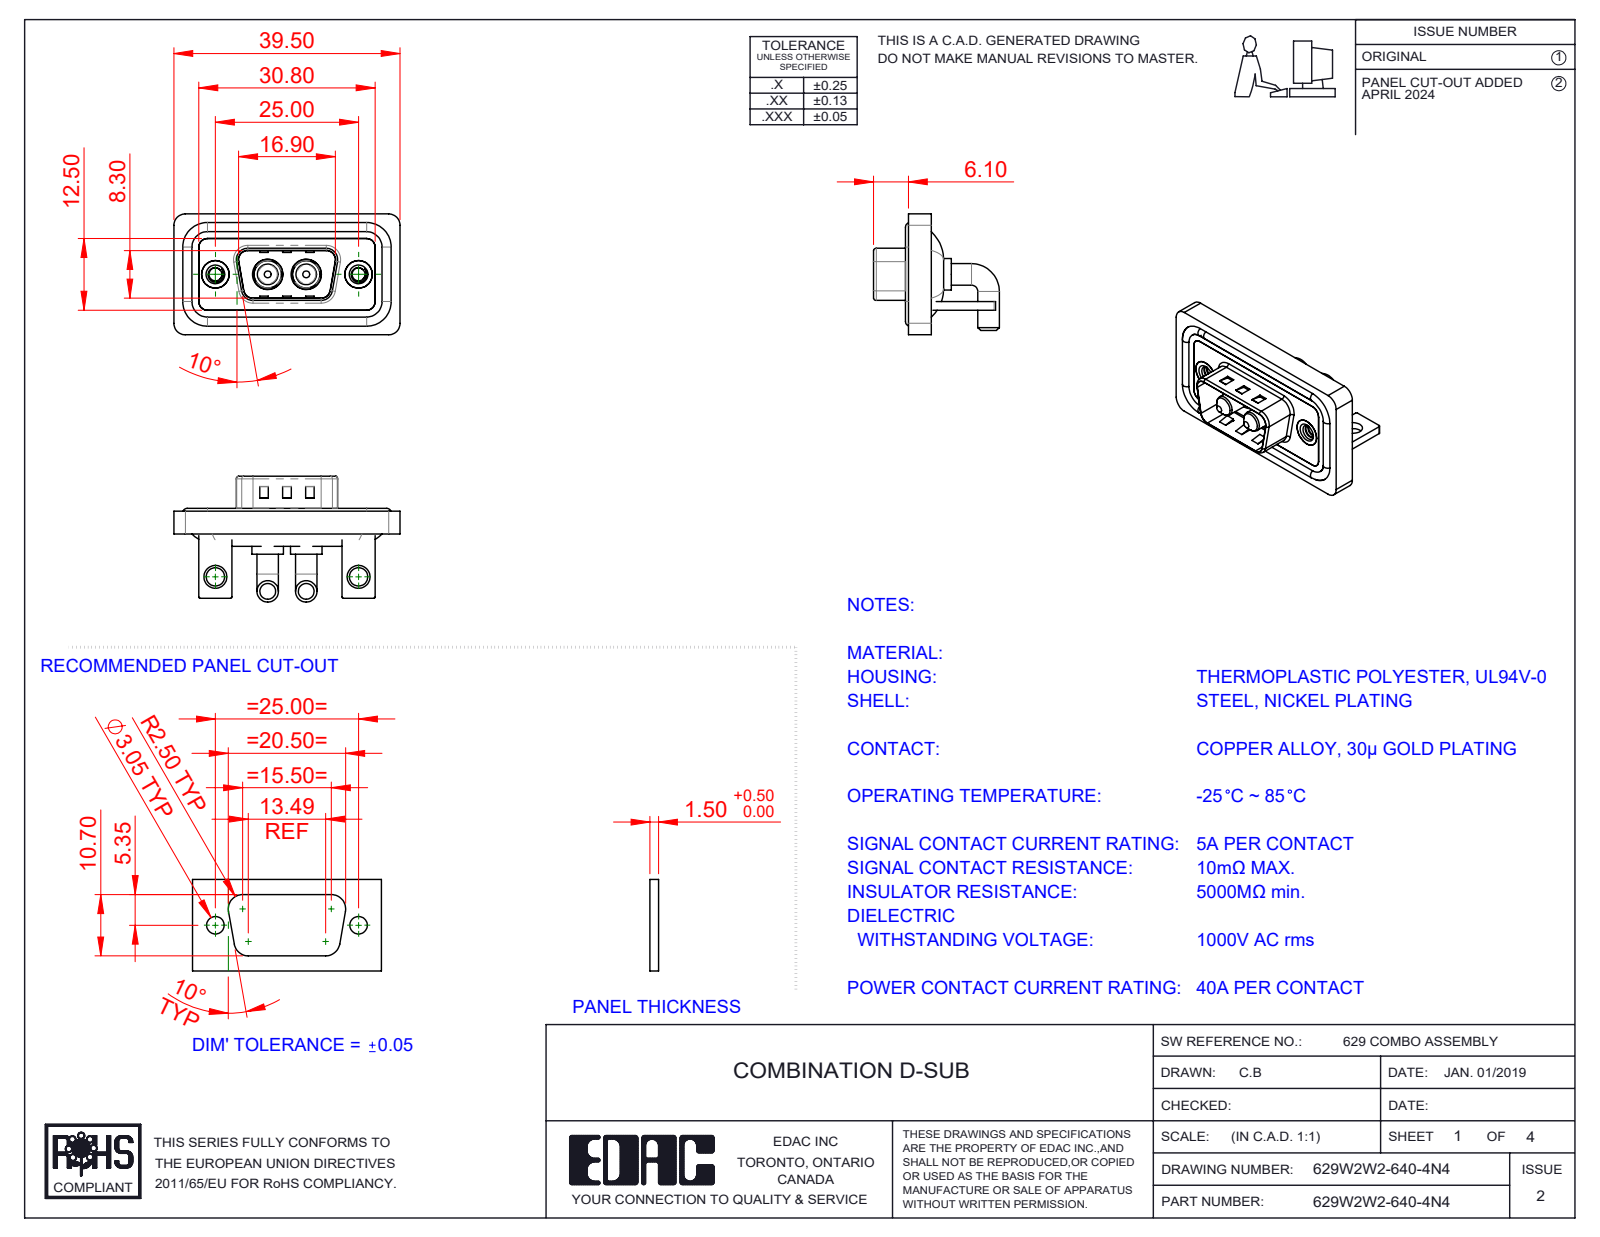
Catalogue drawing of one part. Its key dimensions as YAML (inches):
part_name: "629Combo Housing_2W2; 629Combo Stabilizer Bracket; 629Combo Waterproof Housing_09 Contacts; 629Combo Threaded Rivet_3 (+4 more)"
step_written_by: "SolidWorks 2023 (CONFIG_CONTROL_DESIGN)"
units: inches
bodies: {solids: 13, faces: 537, planar: 185, cylindrical: 240, other: 112}
overall_size: [1.555, 0.865, 0.831]
volume: 0.306
surface_area: 12.16
round_holes:
  - {diameter: 0.089, count: 2}
  - {diameter: 0.126, count: 2}
  - {diameter: 0.157, count: 2}
  - {diameter: 0.189, count: 2}
  - {diameter: 0.191, count: 2}
  - {diameter: 0.197, count: 2}
  - {diameter: 0.209, count: 2}
round_bosses_or_shafts:
  - {diameter: 0.148, count: 4}
  - {diameter: 0.063, count: 4}
  - {diameter: 0.217, count: 2}
  - {diameter: 0.205, count: 2}
  - {diameter: 0.193, count: 2}
  - {diameter: 0.187, count: 2}
  - {diameter: 0.142, count: 2}
partial_cylinders:
  - {radius: 0.079, count: 19}
  - {radius: 0.059, count: 18}
  - {radius: 0.01, count: 16}
  - {radius: 0.02, count: 9}
  - {radius: 0.063, count: 8}
  - {radius: 0.024, count: 4}
  - {radius: 0.026, count: 4}
  - {radius: 0.035, count: 4}
face_to_face_distances: [0.016, 0.059, 0.114, 0.031, 0.043, 0.047, 0.083, 0.063, 0.146, 0.098]
hole_center_spacings: [0.36, 0.624, 0.984, 0.265]
